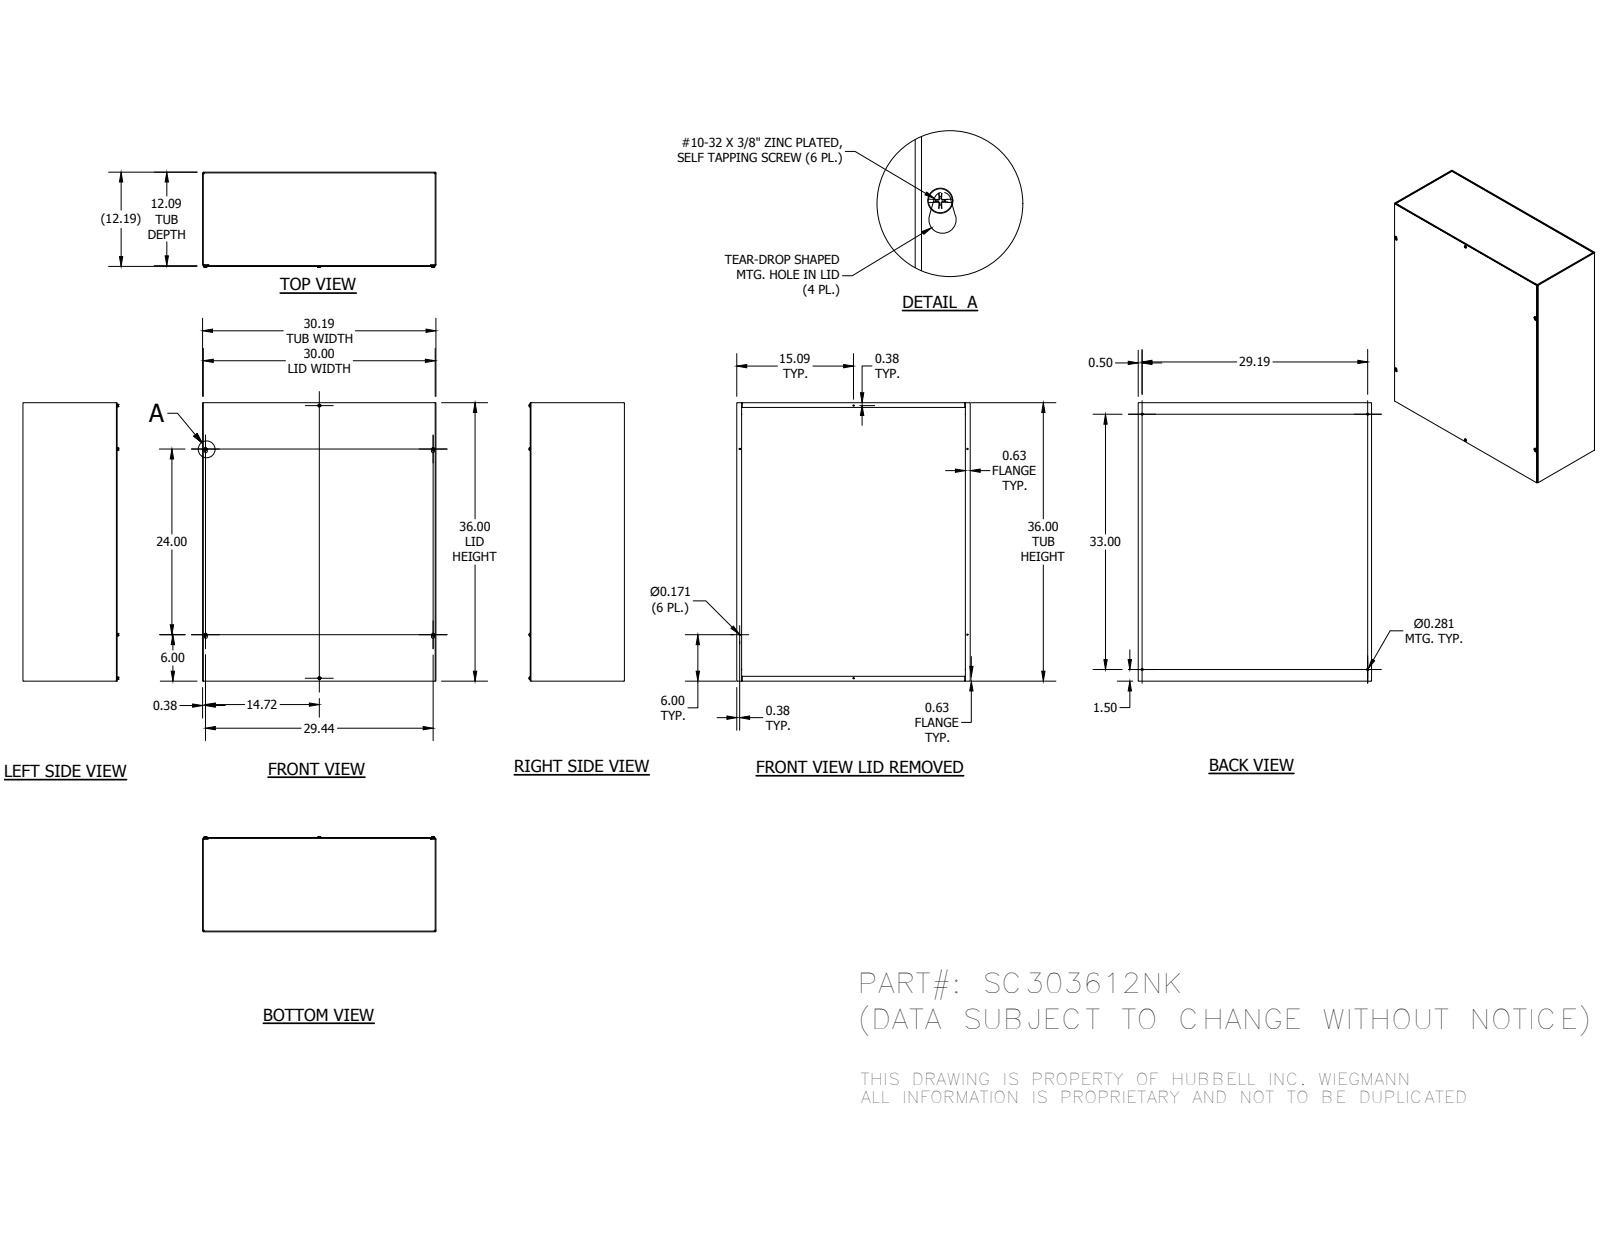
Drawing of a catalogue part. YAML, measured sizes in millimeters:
part_name: "SC303612NKBLR; SC3012NKTB; SC3036LPA; 37214 (+1 more)"
step_written_by: "Autodesk Inventor 2014 (AUTOMOTIVE_DESIGN)"
units: millimeters
bodies: {solids: 10, faces: 404, planar: 232, cylindrical: 50, other: 122}
overall_size: [914.4, 766.76, 312.91]
volume: 5942000
surface_area: 5022000
round_holes:
  - {diameter: 4.34, count: 6}
  - {diameter: 7.14, count: 4}
  - {diameter: 7.92, count: 2}
round_bosses_or_shafts:
  - {diameter: 4.83, count: 6}
partial_cylinders:
  - {radius: 0.4, count: 12}
  - {radius: 2.78, count: 12}
  - {radius: 3.17, count: 4}
  - {radius: 5.16, count: 4}
face_to_face_distances: [2.38, 307.18, 304.8, 309.56, 764.38, 912.02, 762, 766.76, 914.4, 909.64]
hole_center_spacings: [114.34, 371.78, 400.23, 723.91, 753.26, 840.24, 942.71, 1038.45]
